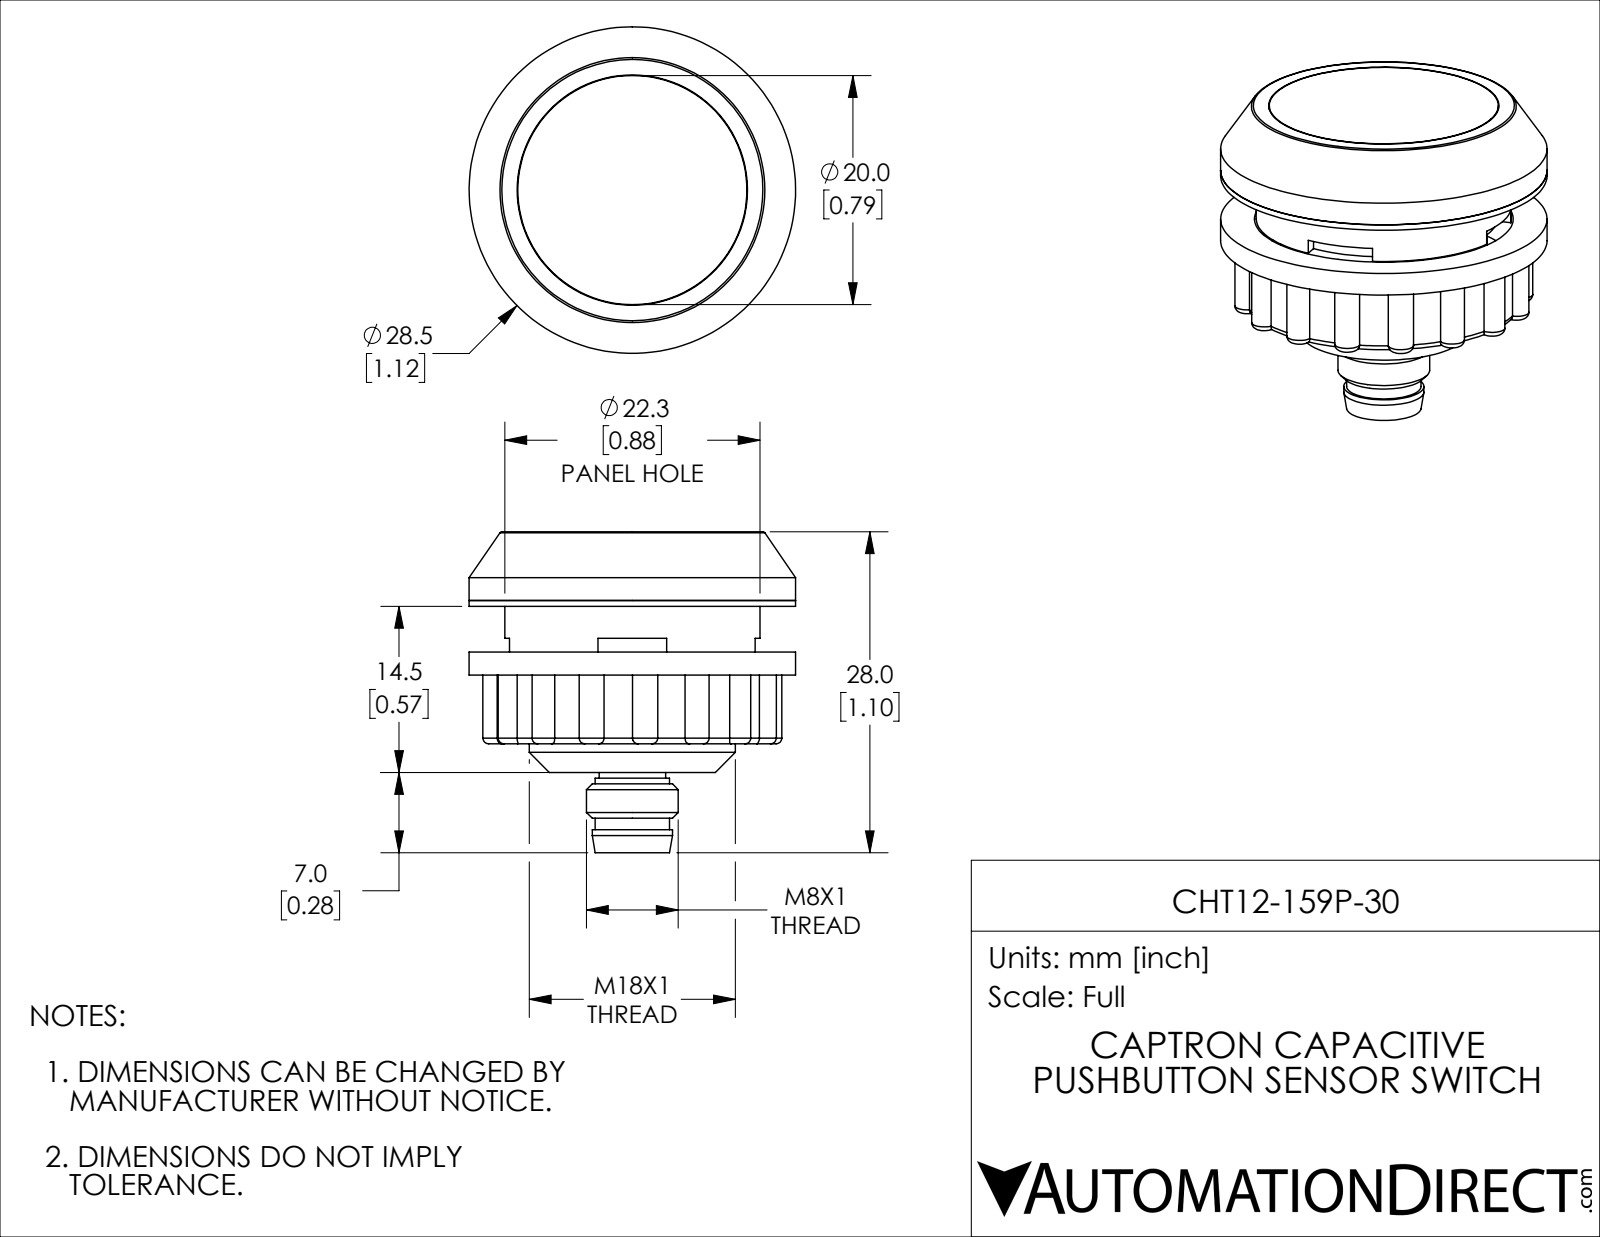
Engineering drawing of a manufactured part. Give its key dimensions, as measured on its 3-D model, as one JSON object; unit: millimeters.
{"part_name": "CHT12-159P-30", "step_written_by": "SolidWorks 2019 (CONFIG_CONTROL_DESIGN)", "units": "millimeters", "bodies": {"solids": 10, "faces": 212, "planar": 40, "cylindrical": 97, "other": 75}, "overall_size": [28.5, 28.5, 28], "volume_mm3": 10506, "surface_area_mm2": 7381, "round_holes": [[2, 2], [6, 1], [17, 1], [20.1, 1], [22.22, 1], [22.6, 1]], "round_bosses_or_shafts": [[1, 4], [28.5, 1], [22.28, 1], [19.08, 1], [18, 1], [8, 1], [7, 1], [6.5, 1]], "partial_cylinders_radius": [[1.1, 16], [9.9, 1], [12, 1]], "face_to_face_distances": [3, 6, 0.5, 6.5, 3.5, 10.5, 4, 2.5, 4.5, 15], "hole_center_spacings": [5.5, 11]}
